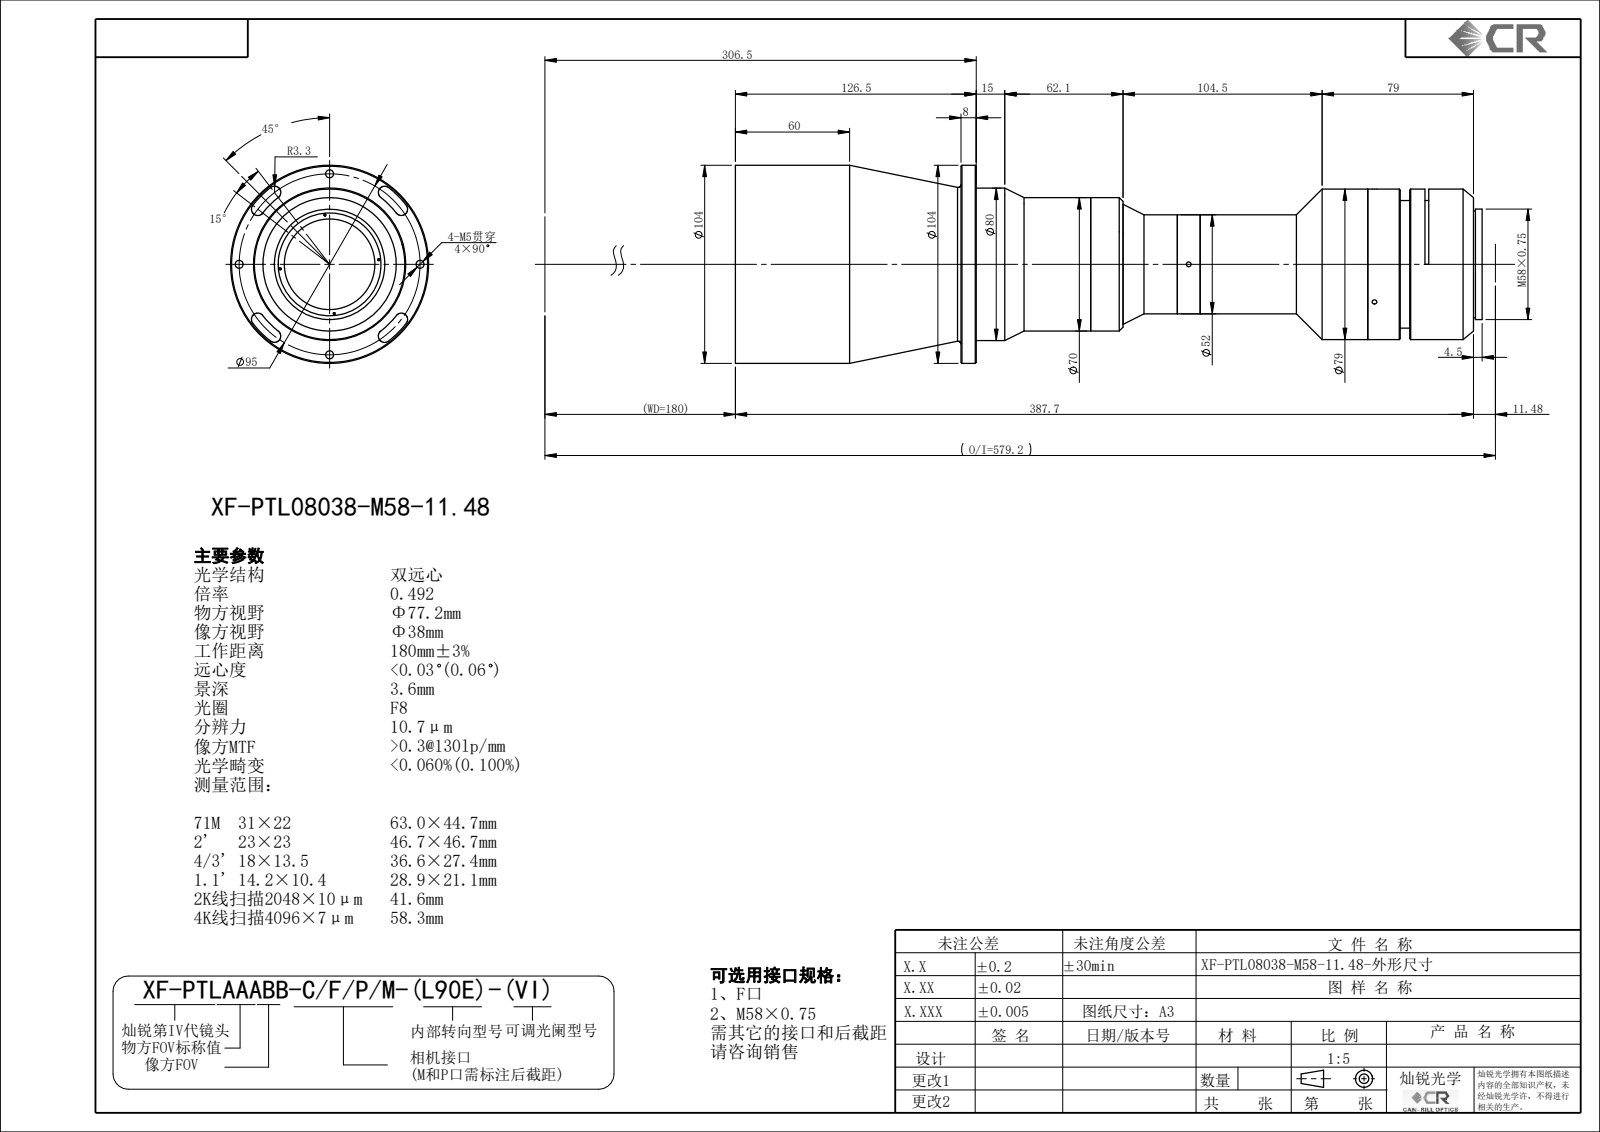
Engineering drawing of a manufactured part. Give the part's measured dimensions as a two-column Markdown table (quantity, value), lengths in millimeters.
| quantity | value |
| --- | --- |
| part name | XF-PTL08038-M58-11.48 |
| STEP written by | SolidWorks 2018 (CONFIG_CONTROL_DESIGN) |
| units | millimeters |
| bodies | 0 solids, 150 faces (36 planar, 83 cylindrical, 31 other) |
| overall size | 392.18 × 104 × 104 |
| round holes (diameter × count) | 4.2 × 4, 2.5 × 3, 54 × 1, 60 × 1, 63 × 1, 64 × 1, 67 × 1, 94 × 1, 98 × 1 |
| round bosses / shafts (diameter × count) | 104 × 1, 80 × 1, 79 × 1, 70 × 1, 58 × 1, 56 × 1, 52 × 1, 5.5 × 1 |
| partial cylindrical surfaces (radius × count) | 3.3 × 8, 3 × 1, 44.2 × 1, 50.8 × 1 |
| main face-to-face distances | 8, 205.66, 213.66, 235.68, 269.18, 261.18, 55.52, 230.68, 222.68, 17.02 |
| hole center spacings | 47.5, 67.18, 95 |
